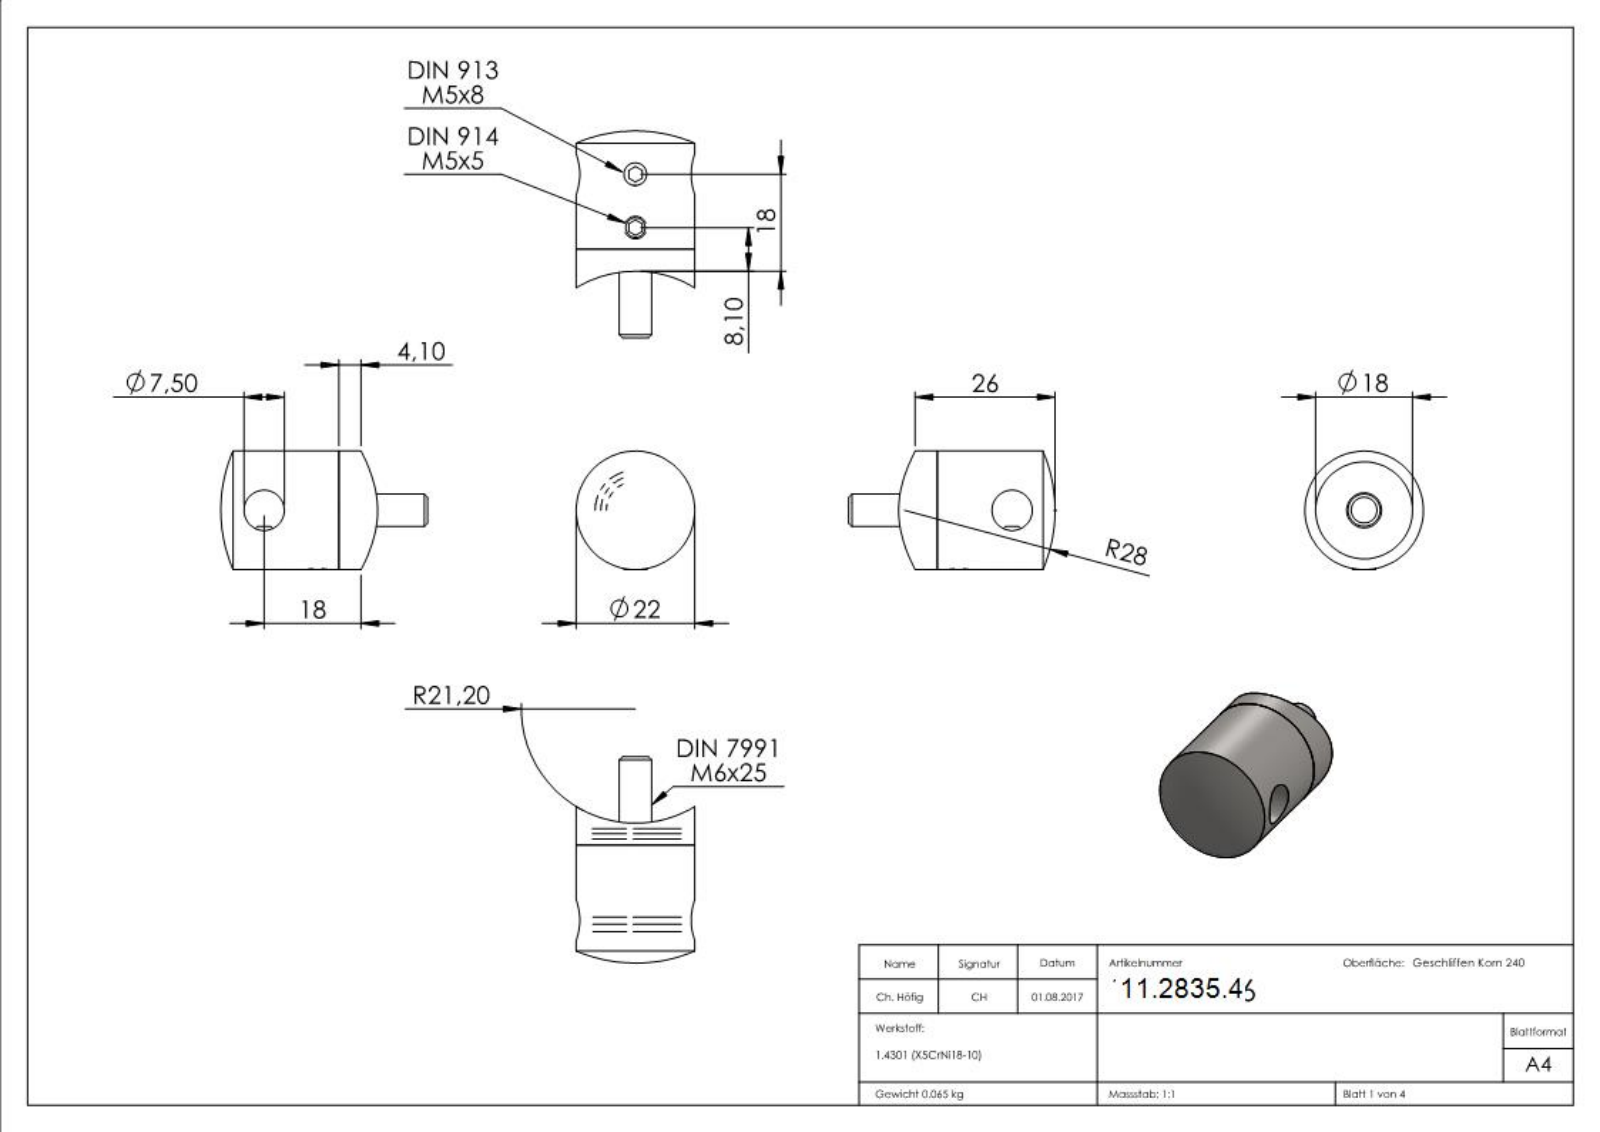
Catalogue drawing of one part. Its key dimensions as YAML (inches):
part_name: "DIN 914 M5x5_DIN914 M5x5; 100021006; DIN913 M5x8_DIN913 M5x8; DIN7991 M6x25 (+7 more)"
step_written_by: "SolidWorks 2018 (CONFIG_CONTROL_DESIGN)"
units: inches
bodies: {solids: 5, faces: 74, planar: 35, cylindrical: 15, other: 24}
overall_size: [3.228, 1.319, 0.866]
volume: 0.549
surface_area: 9.426
round_holes:
  - {diameter: 0.165, count: 2}
  - {diameter: 0.256, count: 1}
  - {diameter: 0.402, count: 1}
  - {diameter: 0.476, count: 1}
  - {diameter: 0.709, count: 1}
round_bosses_or_shafts:
  - {diameter: 0.197, count: 2}
  - {diameter: 0.866, count: 1}
  - {diameter: 0.472, count: 1}
  - {diameter: 0.236, count: 1}
partial_cylinders:
  - {radius: 0.835, count: 1}
face_to_face_distances: [0.378, 0.299, 0.079, 1.01, 0.711, 0.632, 0.098, 0.157, 0.026, 0.274]
hole_center_spacings: [0.488]
